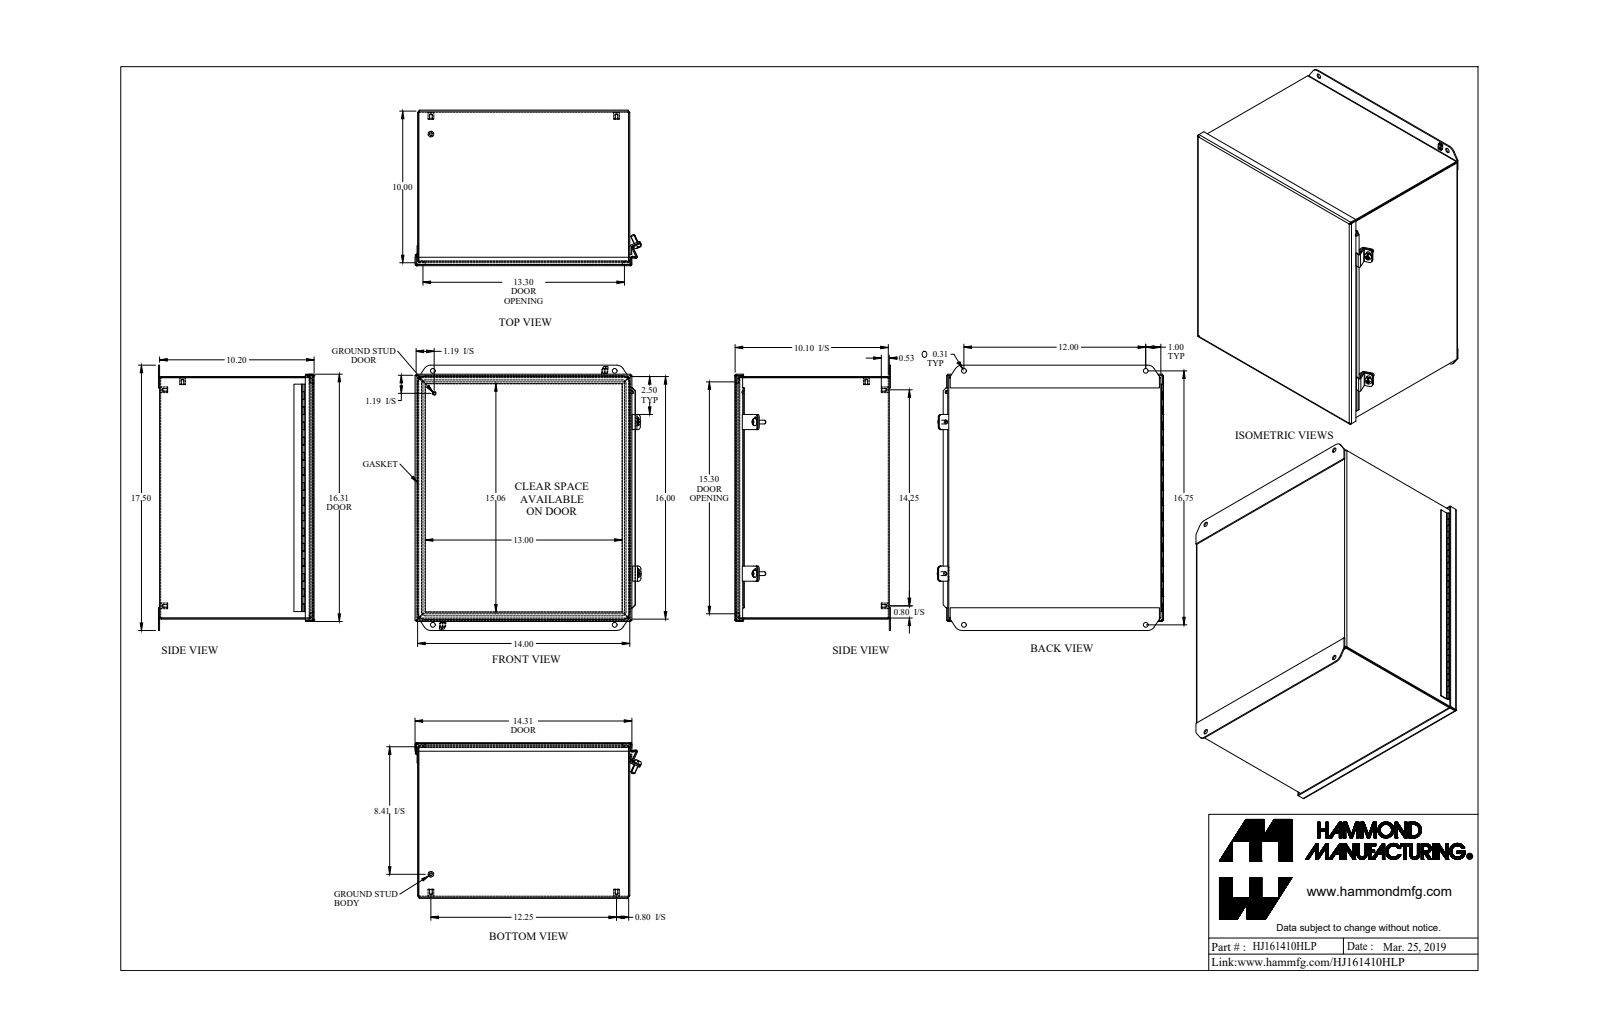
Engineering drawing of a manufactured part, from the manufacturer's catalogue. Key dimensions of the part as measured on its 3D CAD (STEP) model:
Part name (STEP PRODUCT): HJ161410HLP
STEP written by: SolidWorks 2018 (AUTOMOTIVE_DESIGN)
Units: inches
Bodies: 20 solids, 841 faces (446 planar, 267 cylindrical, 128 other)
Overall size (bounding box): 17.5 × 14.937 × 10.269
Volume: 88.6 in³ · Surface area: 2 482 in²
Round holes (diameter × count): ⌀0.156 ×5, ⌀0.313 ×4, ⌀0.213 ×2, ⌀0.05 ×1
Round bosses / shafts (diameter × count): ⌀0.375 ×5, ⌀0.25 ×3, ⌀0.48 ×2, ⌀0.188 ×1, ⌀0.1 ×1, ⌀0.045 ×1
Partial cylindrical surfaces — rounded edges, fillets, slot ends (radius × count): R0.25 ×16, R0.036 ×13, R0.108 ×13, R0.188 ×8, R0.01 ×4, R0.029 ×4, R0.086 ×4, R0.141 ×4
Main face-to-face distances: 0.072, 10.125, 13.928, 15.928, 10.197, 10.053, 13.856, 14, 16, 15.856
Hole centre spacings: 1.256, 12.189, 15.5, 19.679, 12, 12.25, 14.25, 16.75
